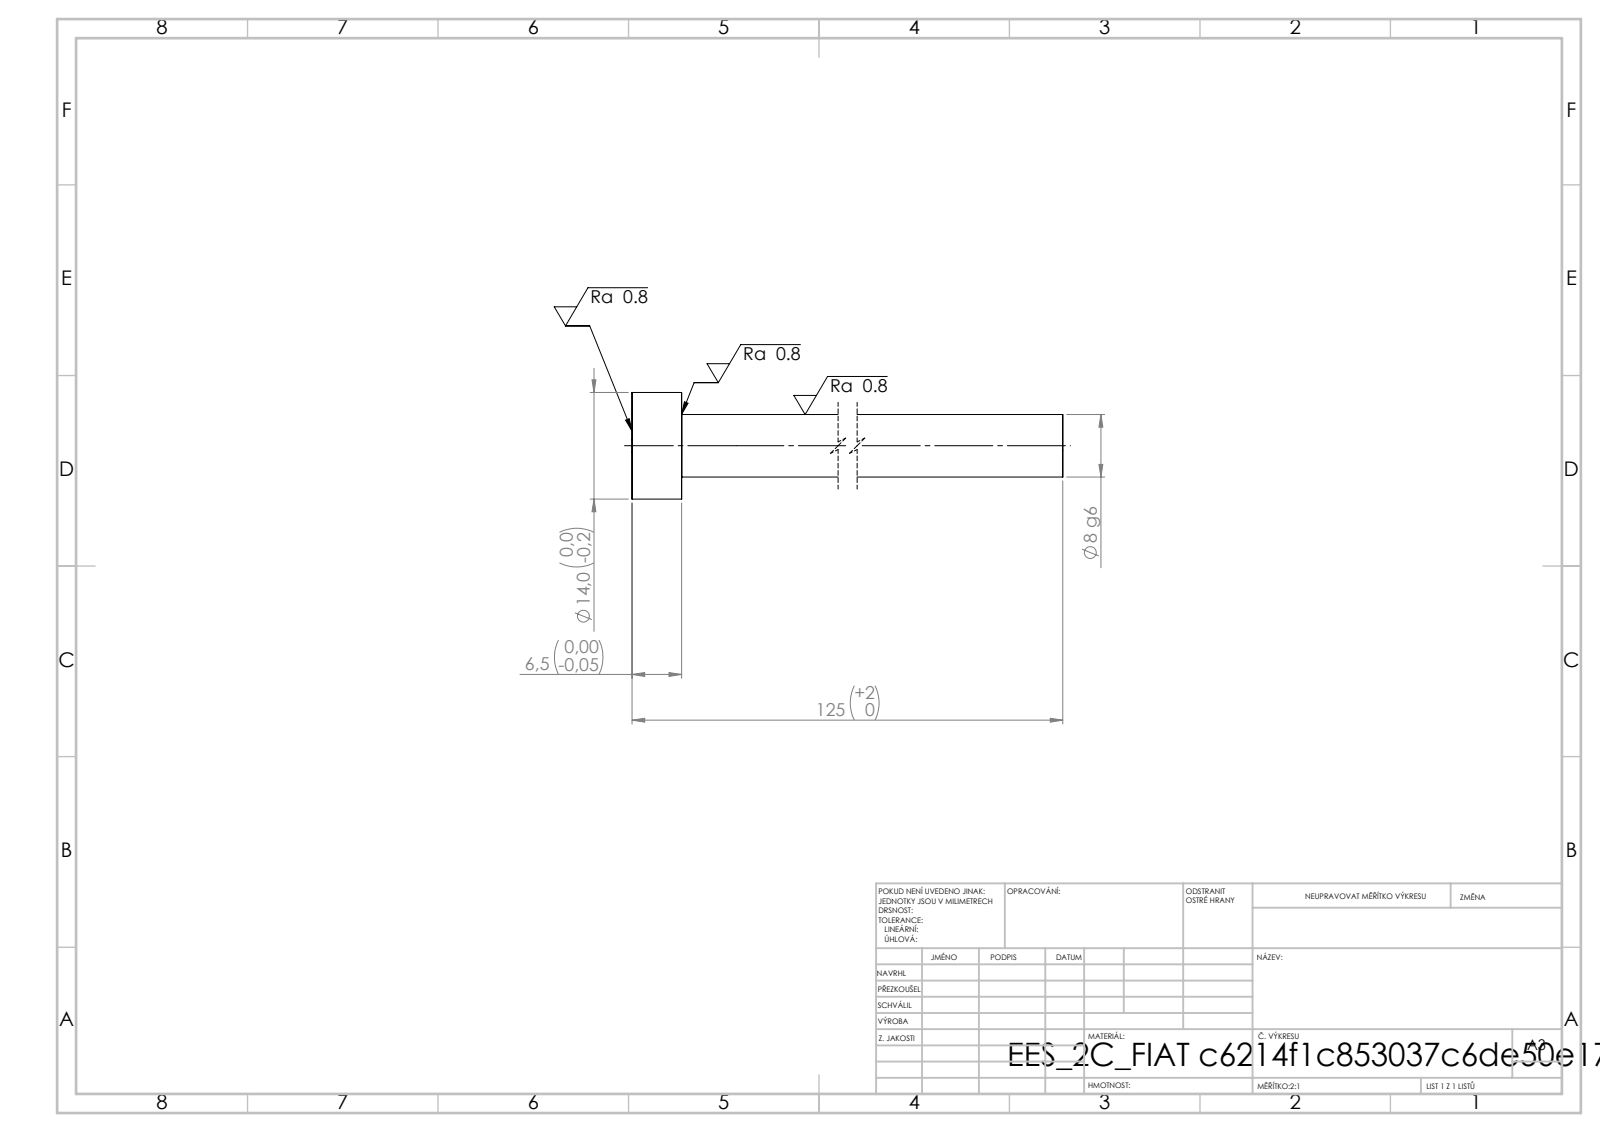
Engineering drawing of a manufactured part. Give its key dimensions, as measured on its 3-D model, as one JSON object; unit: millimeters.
{"step_written_by": "SolidWorks 2019 (CONFIG_CONTROL_DESIGN)", "units": "millimeters", "bodies": {"solids": 1, "faces": 7, "planar": 3, "cylindrical": 4, "other": 0}, "overall_size": [125, 14, 14], "volume_mm3": 7259, "surface_area_mm2": 3646, "round_bosses_or_shafts": [[14, 1], [8.2, 1]], "face_to_face_distances": [6.5, 125, 118.5]}
